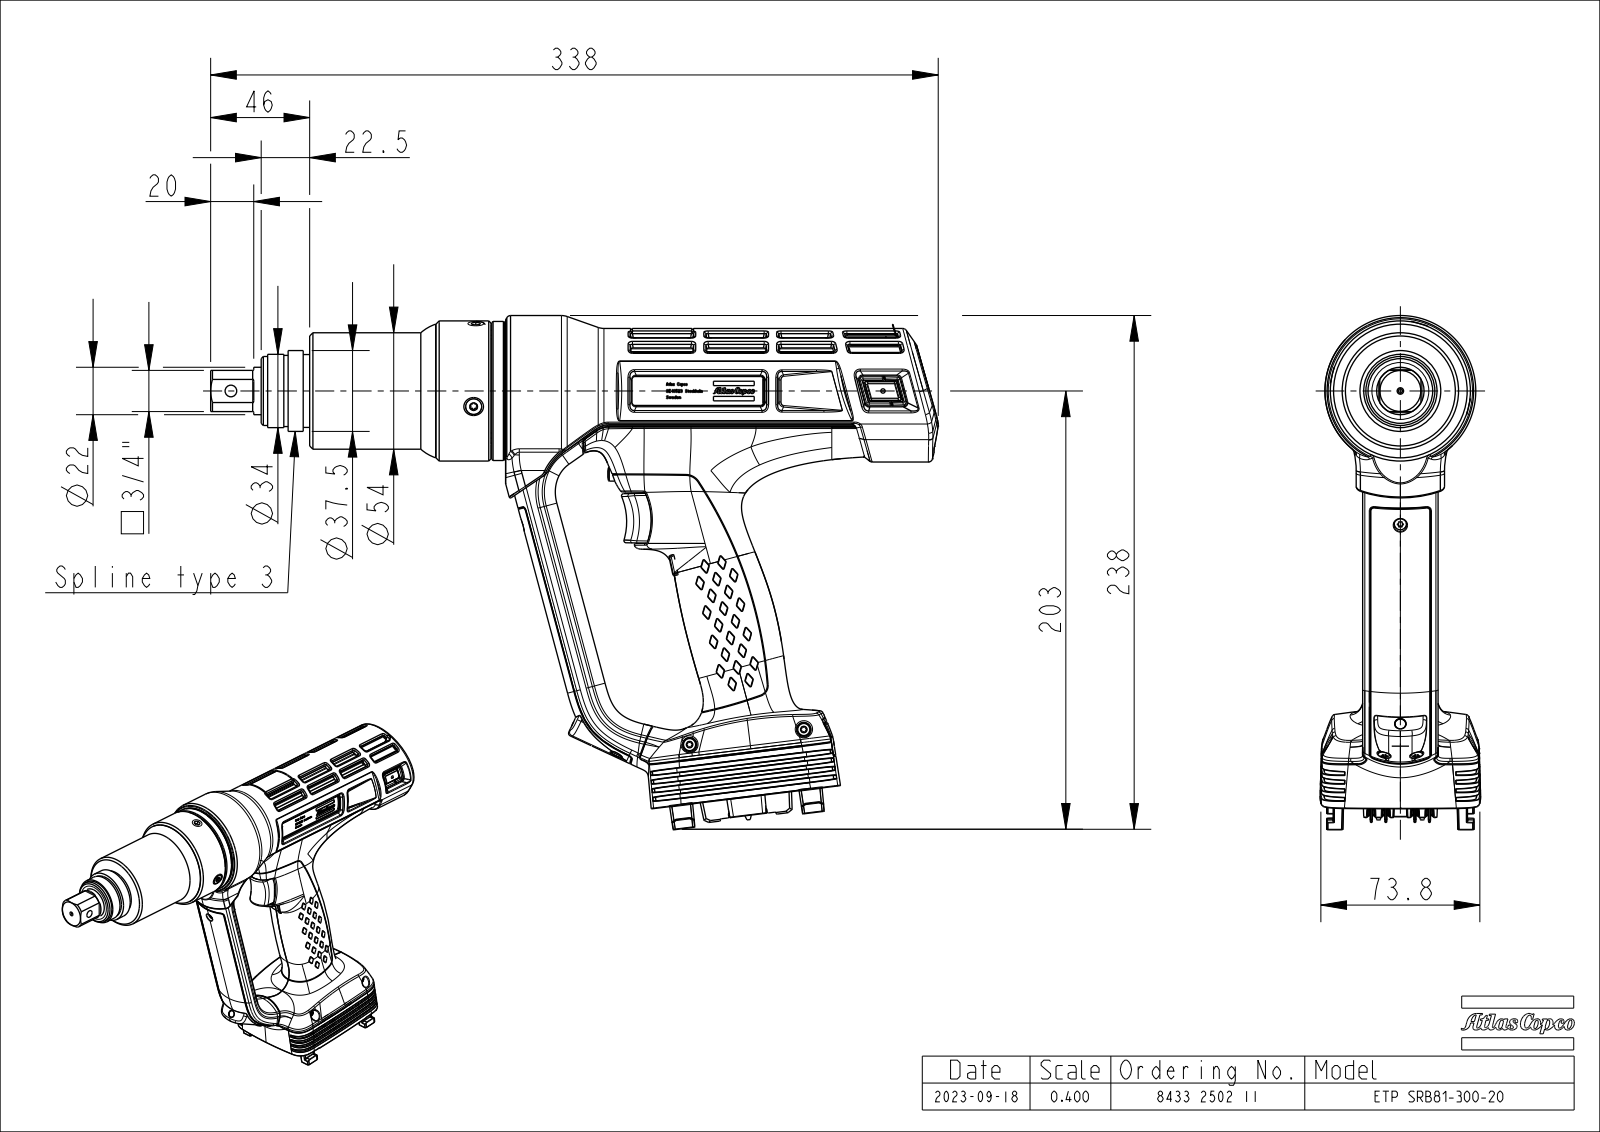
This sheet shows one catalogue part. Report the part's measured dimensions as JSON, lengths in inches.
{"part_name": "EXT_COMP_SW0008", "step_written_by": "CREO PARAMETRIC BY PTC INC, 2018100 (CONFIG_CONTROL_DESIGN)", "units": "inches", "bodies": {"solids": 5, "faces": 7956, "planar": 2838, "cylindrical": 1479, "other": 3639}, "overall_size": [13.293, 9.256, 2.935], "volume_in3": 70.53, "surface_area_in2": 322.9, "round_holes": [[0.118, 3], [0.138, 2], [0.161, 2], [0.079, 1], [0.213, 1], [0.394, 1]], "round_bosses_or_shafts": [[0.295, 2], [0.22, 2], [0.157, 2], [2.559, 1], [2.52, 1], [2.441, 1], [2.126, 1], [1.476, 1]], "partial_cylinders_radius": [[0.012, 411], [0.02, 252], [0.039, 40], [0.02, 36], [0.011, 34], [0.004, 32], [0.031, 22], [0.079, 19]], "face_to_face_distances": [0.236, 0.016, 0.453, 0.217, 0.252, 0.469, 0.039, 0.797, 0.266, 1.541], "hole_center_spacings": [0.89]}
